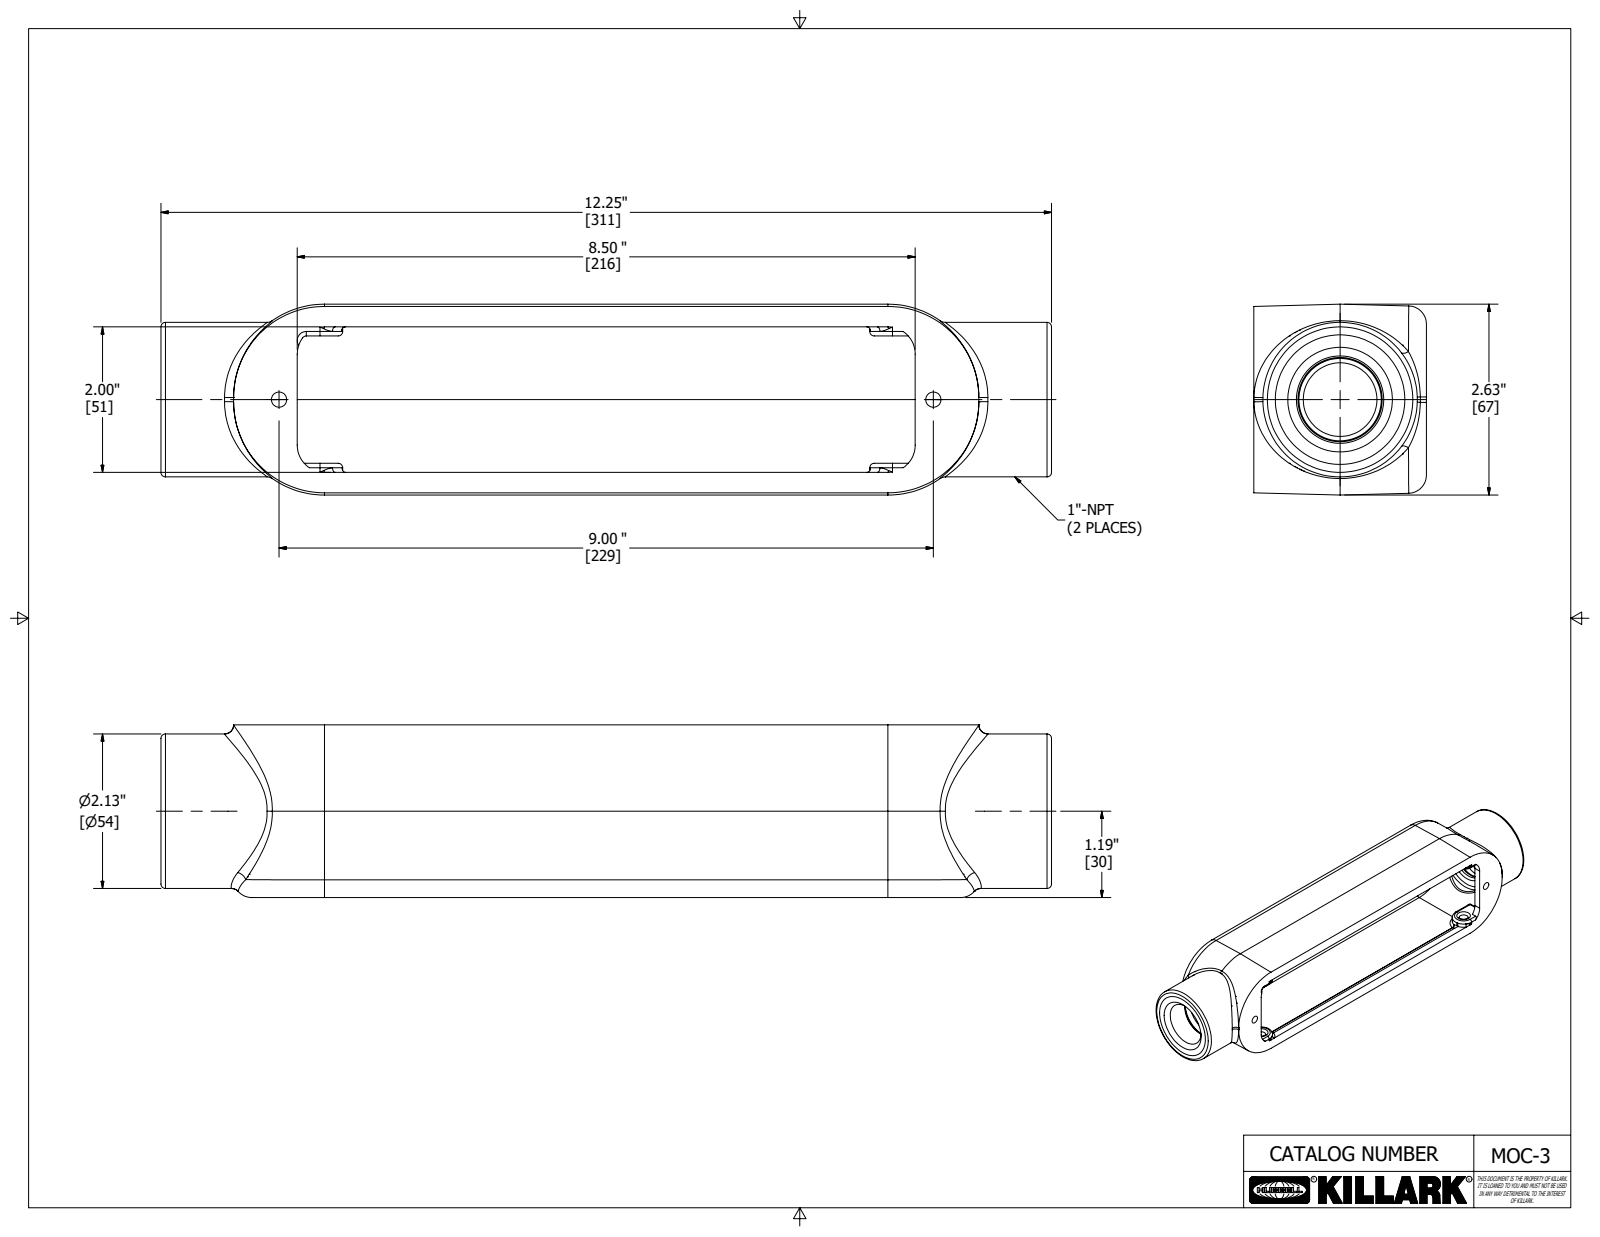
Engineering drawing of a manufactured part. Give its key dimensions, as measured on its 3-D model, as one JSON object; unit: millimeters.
{"part_name": "21278", "step_written_by": "Autodesk Inventor 2020 (AUTOMOTIVE_DESIGN)", "units": "millimeters", "bodies": {"solids": 1, "faces": 240, "planar": 48, "cylindrical": 73, "other": 119}, "overall_size": [311.2, 66.7, 60.3], "volume_mm3": 317600, "surface_area_mm2": 117000, "round_holes": [[5.3, 2], [6.4, 2], [25.7, 1], [30.5, 1], [33.6, 1]], "round_bosses_or_shafts": [[54, 1]], "partial_cylinders_radius": [[1.6, 11], [31.8, 8], [3.2, 6], [0.8, 5], [6.4, 4], [9.5, 4], [25.4, 4], [8, 2]], "face_to_face_distances": [66.7, 57.2, 60.3, 4.7, 3.2, 54, 55.5, 50.8, 30.1, 281], "hole_center_spacings": [200, 228.6]}
